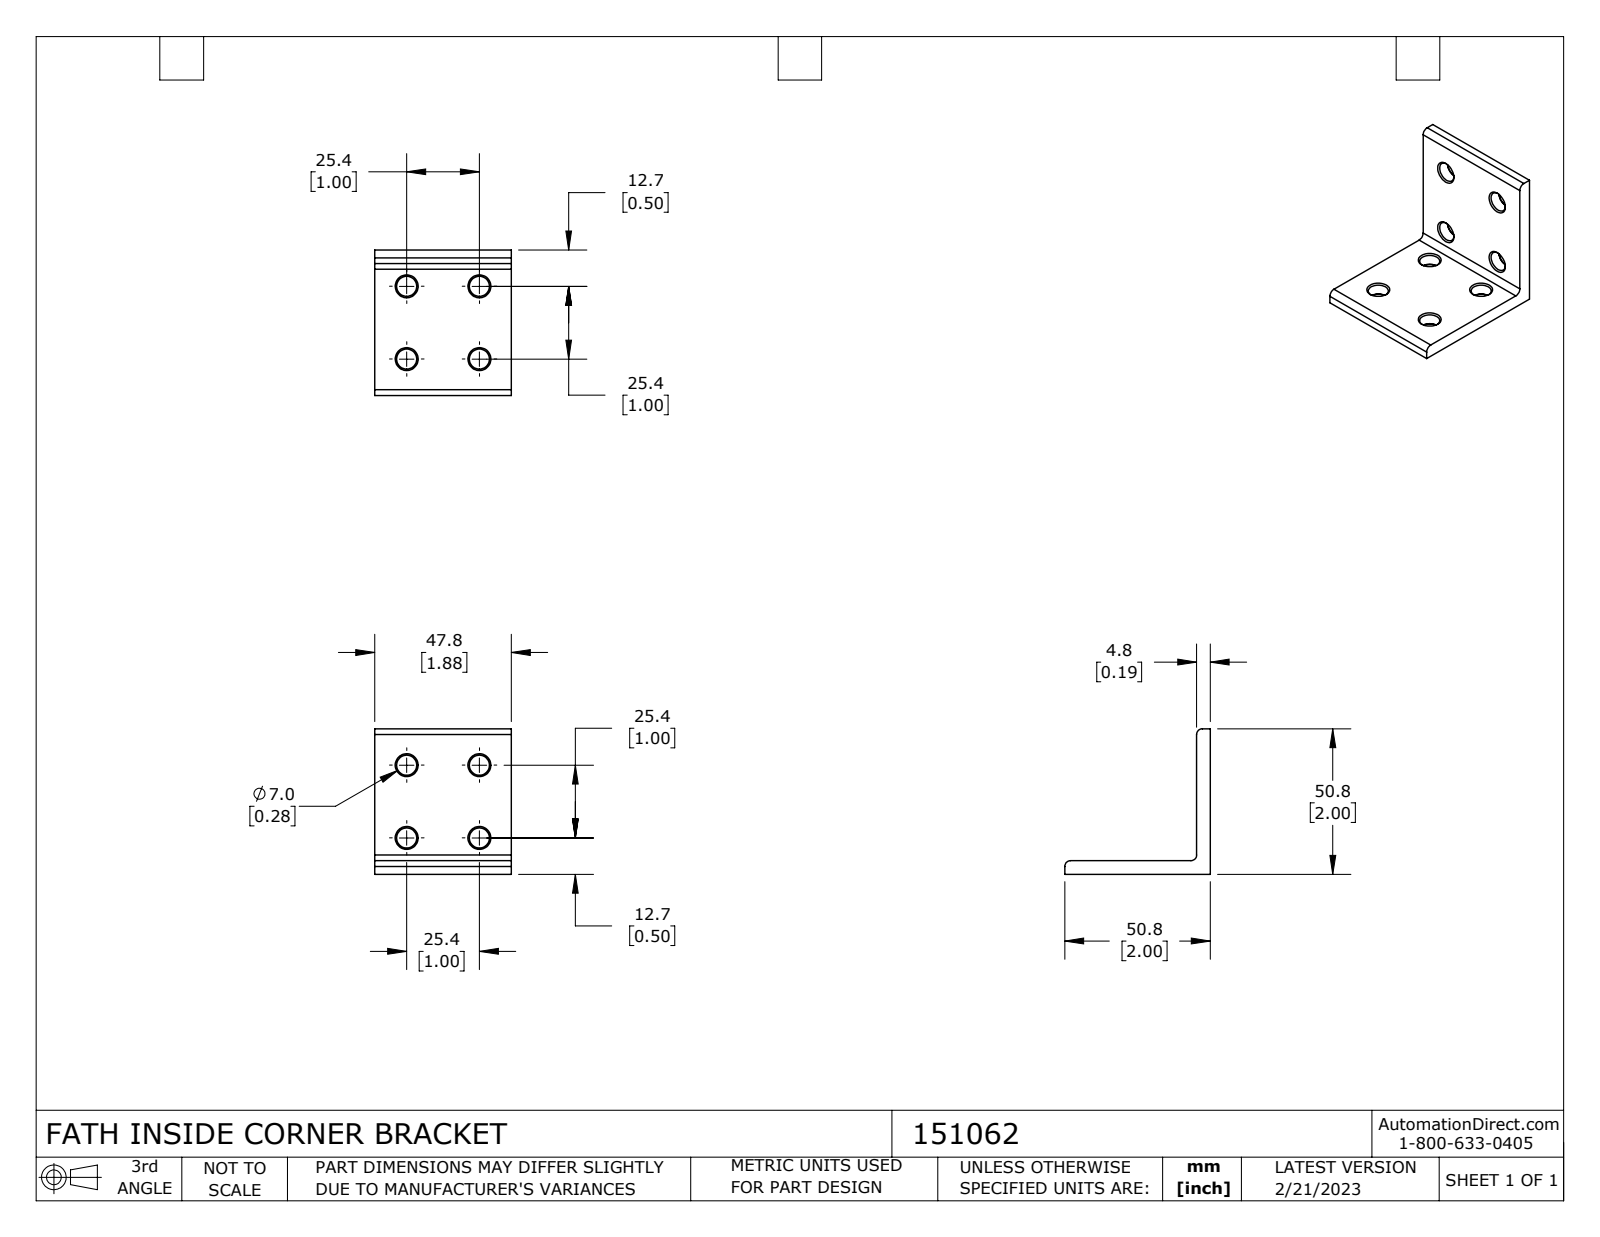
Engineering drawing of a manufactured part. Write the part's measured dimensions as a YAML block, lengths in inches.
part_name: "151062"
step_written_by: "SolidWorks 2021 (CONFIG_CONTROL_DESIGN)"
units: inches
bodies: {solids: 1, faces: 59, planar: 8, cylindrical: 19, other: 32}
overall_size: [2, 2, 1.88]
volume: 1.249
surface_area: 16.47
round_holes:
  - {diameter: 0.276, count: 8}
partial_cylinders:
  - {radius: 0.079, count: 3}
face_to_face_distances: [0.187, 1.88, 2, 1.813]
hole_center_spacings: [1, 1.414]
